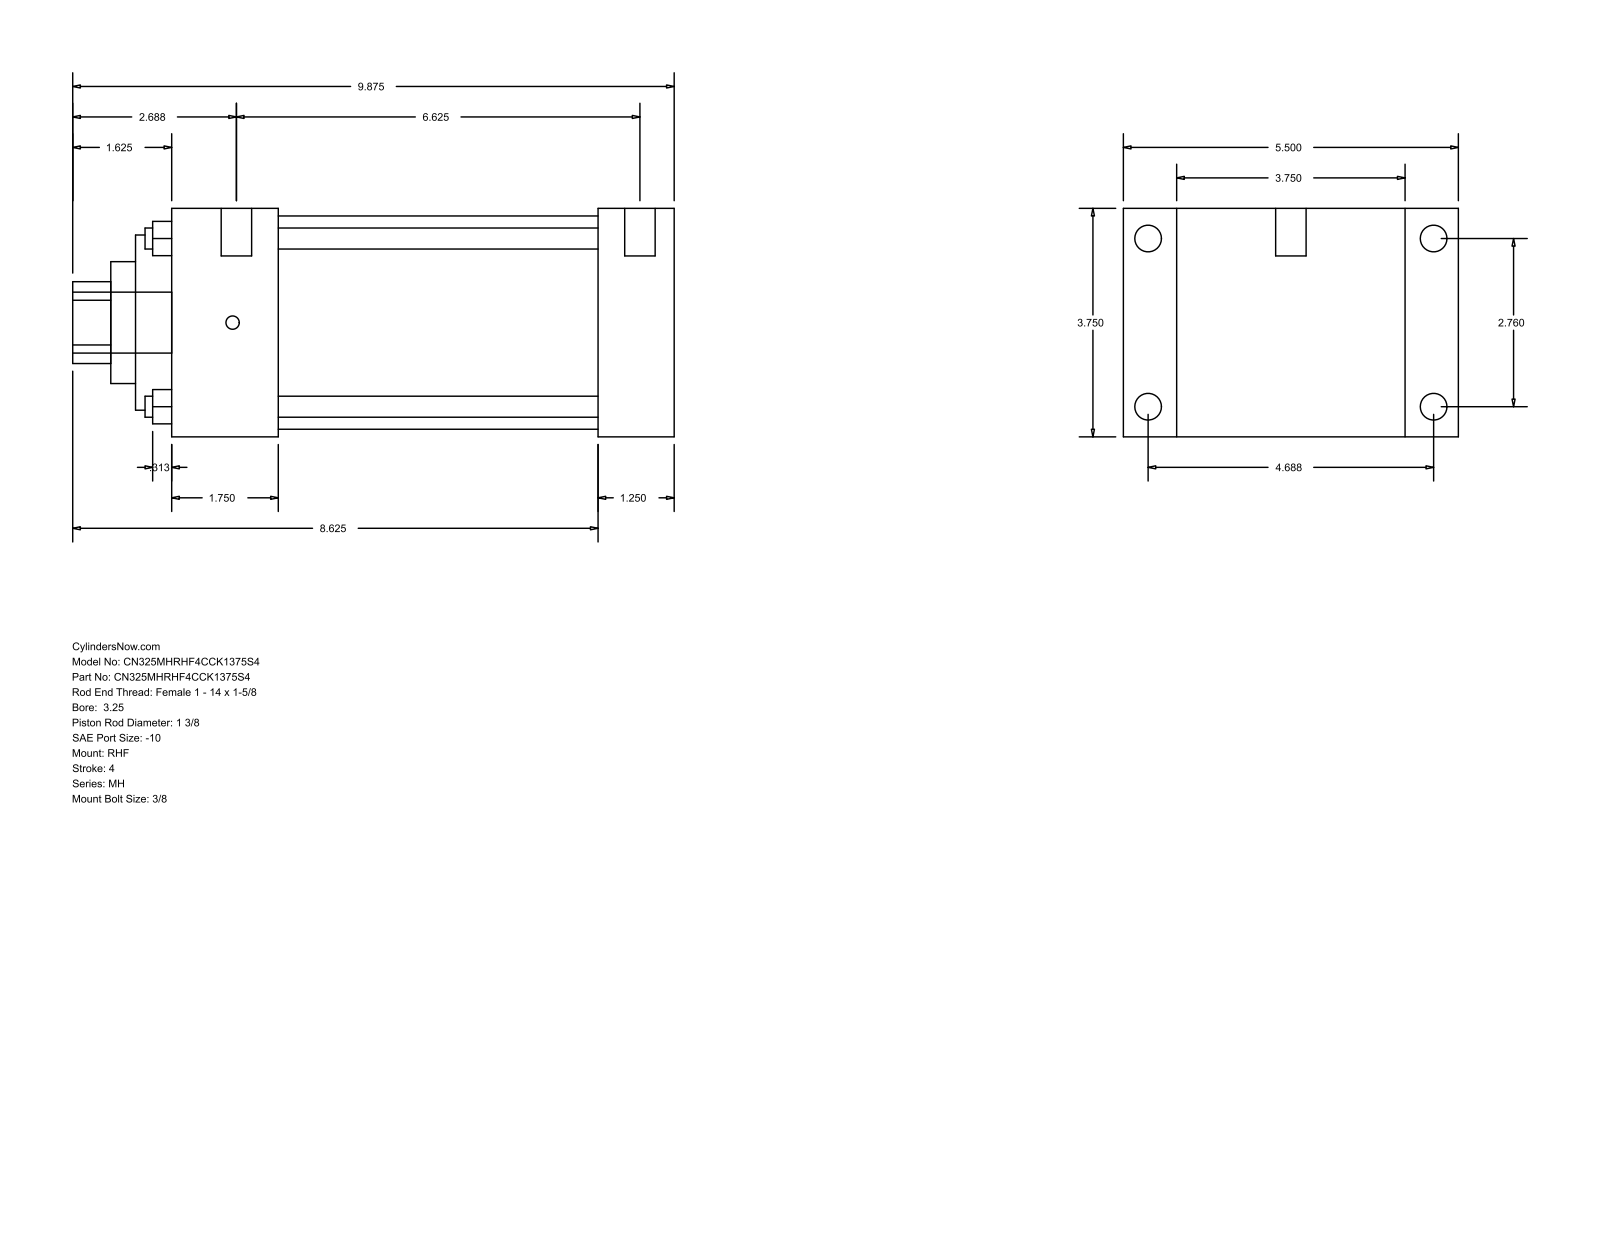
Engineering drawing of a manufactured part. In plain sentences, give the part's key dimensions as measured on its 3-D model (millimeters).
The part is named "MH_RHF__0325_1.375". Its 3-D file was written by "GSSL Pune (CONFIG_CONTROL_DESIGN)". It is 0 solids with 90 faces: 61 planar, 29 cylindrical and 0 other. Overall it measures 250.82 by 139.7 by 95.25 millimeters. Round holes: 4 of diameter 8.76, 1 of diameter 34.92, 1 of diameter 50.8, 1 of diameter 73.03, 1 of diameter 88.9. Round bosses or shafts: 4 of diameter 11.13, 4 of diameter 5.56, 2 of diameter 12.7, 1 of diameter 25.4. Partial cylindrical surfaces (rounded edges, fillets, slot ends): 1 of radius 17.06. The main face-to-face distances are 95.24, 31.75, 22.23, 117.47, 177.8, 209.55, 139.7, 44.45, 133.35, 165.1. The hole center spacings are 49.57, 70.1, 99.14.
